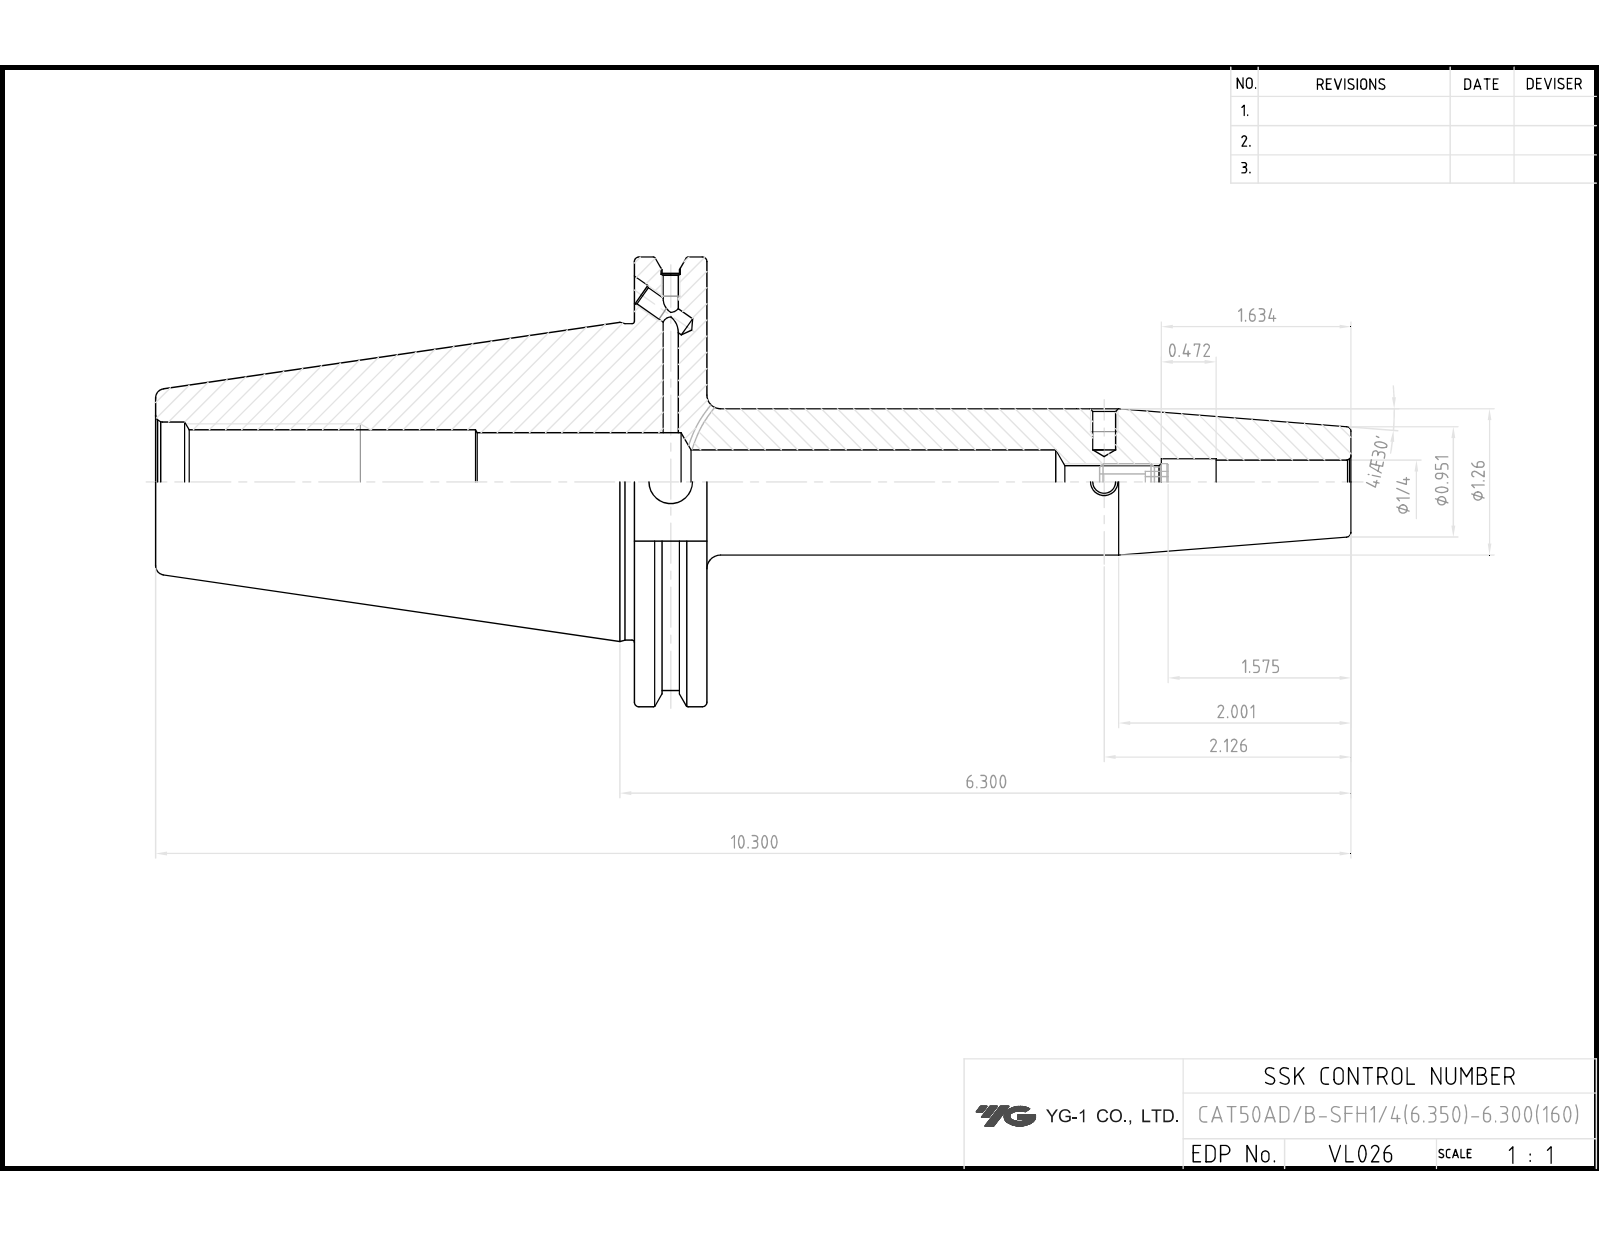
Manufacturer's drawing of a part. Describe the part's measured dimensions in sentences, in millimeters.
The part is named "LO-CAT50ADB-SFH6.35-160". Its 3-D file was written by "Autodesk Inventor 2025 (AUTOMOTIVE_DESIGN)". It is 1 solid with 86 faces: 37 planar, 27 cylindrical and 22 other. Overall it measures 261.6 by 98.42 by 94.69 millimeters. Its volume is 388 529 cubic millimeters and its surface area 59 719 square millimeters. Round holes: 3 of diameter 4.13, 2 of diameter 3.24, 2 of diameter 4.2, 2 of diameter 5, 1 of diameter 6.35, 1 of diameter 7.55, 1 of diameter 9.53, 1 of diameter 10, 1 of diameter 21.97, 1 of diameter 26.2. Round bosses or shafts: 1 of diameter 98.42, 1 of diameter 91.29, 1 of diameter 69.25, 1 of diameter 27. The main face-to-face distances are 15.88, 104.77, 120.65, 73.03, 25.9, 261.6, 156.83, 140.95, 110.82, 6.05.
